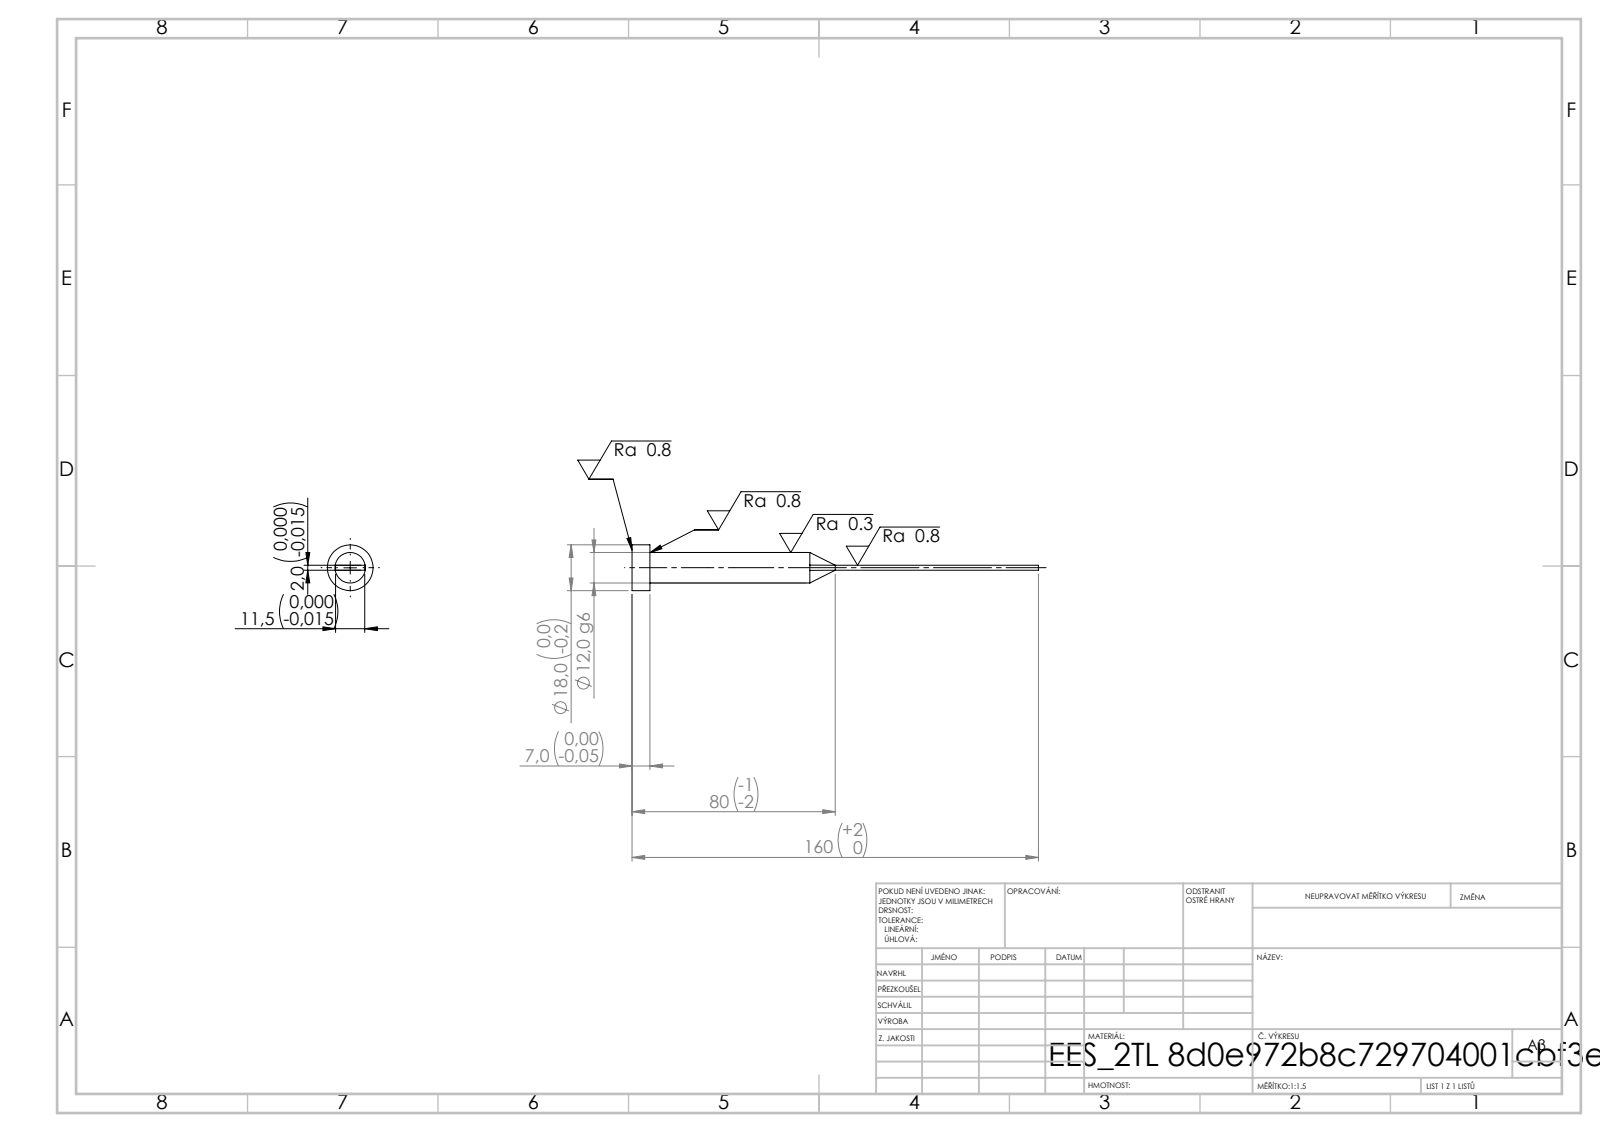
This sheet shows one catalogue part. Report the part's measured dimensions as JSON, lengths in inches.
{"step_written_by": "SolidWorks 2019 (CONFIG_CONTROL_DESIGN)", "units": "inches", "bodies": {"solids": 1, "faces": 15, "planar": 7, "cylindrical": 4, "other": 4}, "overall_size": [6.299, 0.709, 0.709], "volume_in3": 0.695, "surface_area_in2": 8.796, "round_bosses_or_shafts": [[0.709, 1], [0.472, 1]], "face_to_face_distances": [0.079, 0.453, 0.276, 6.299, 6.024]}
